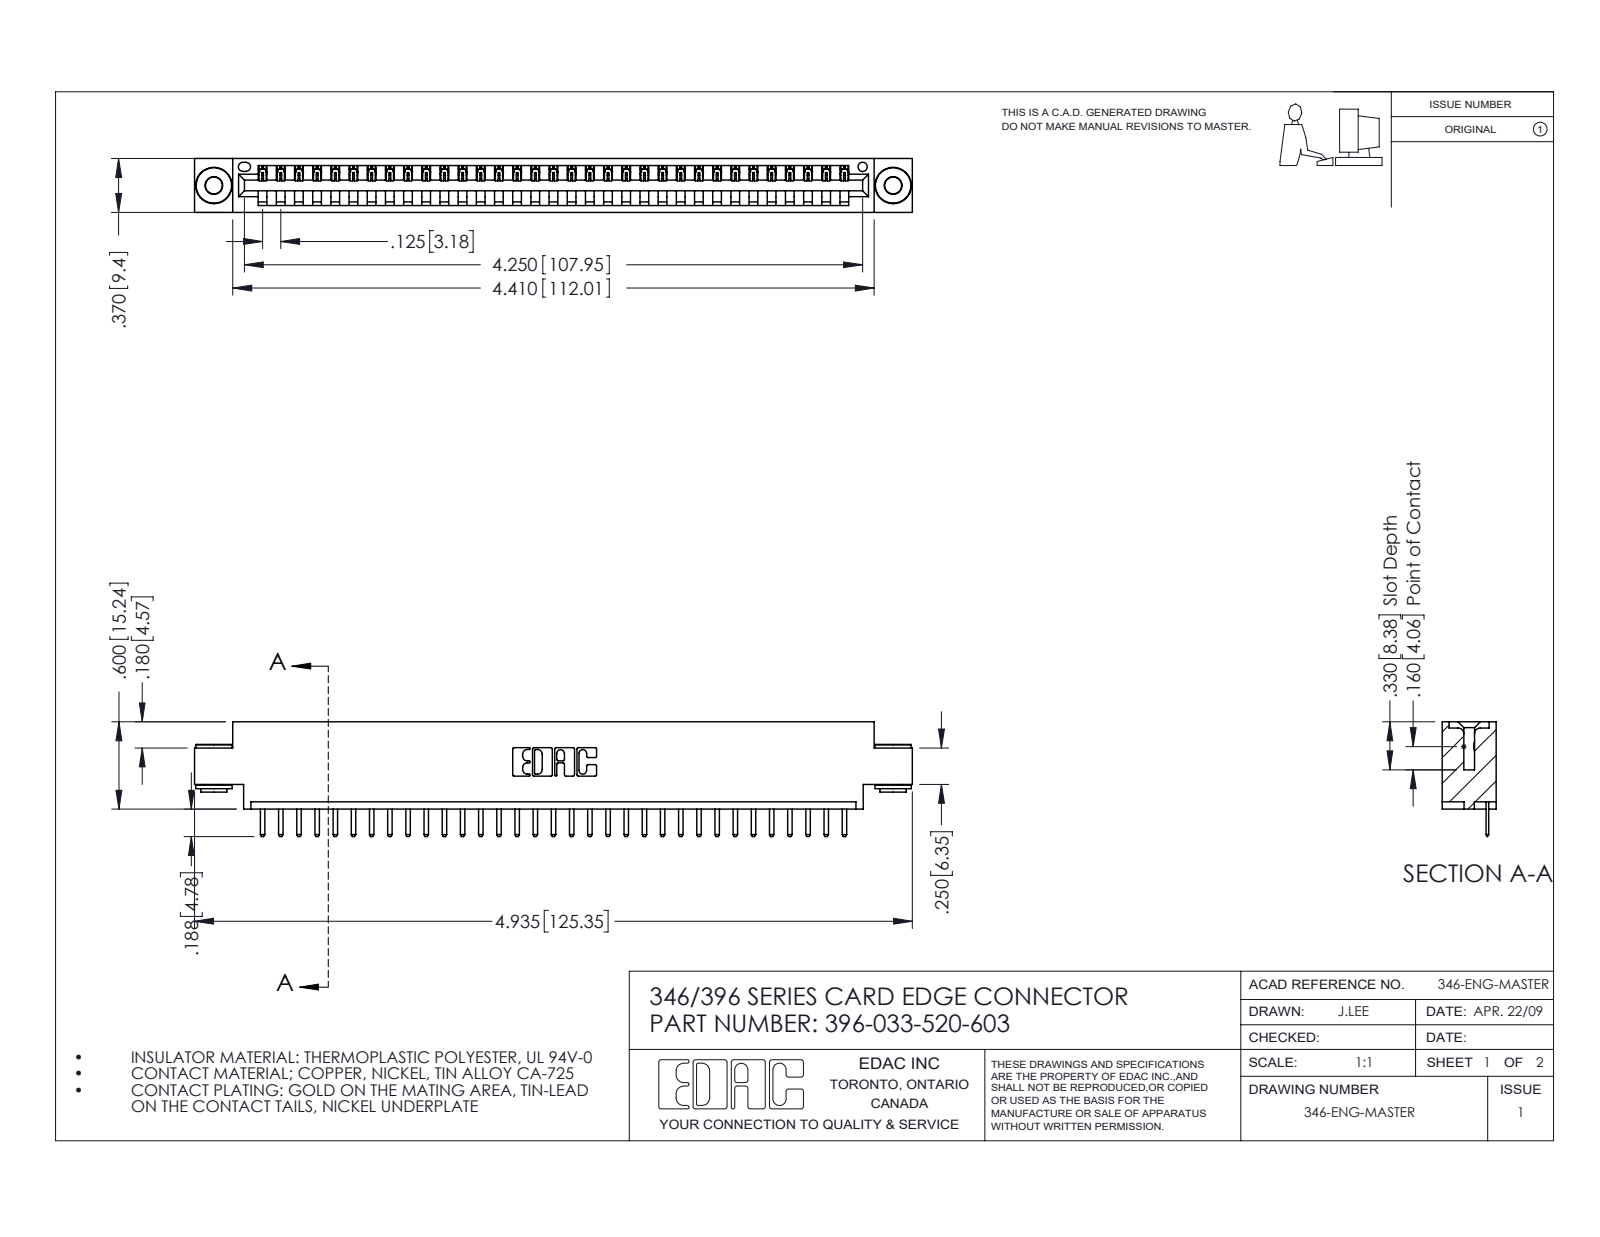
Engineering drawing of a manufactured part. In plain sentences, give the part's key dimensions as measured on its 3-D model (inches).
The part is named "345-250-002_345-250-002-102; 396-033-520-603; 346 Part_0.170 Offset - 0.156 Dia-TH; 345-292-001_345-293-120". Its 3-D file was written by "SolidWorks 2016 (CONFIG_CONTROL_DESIGN)". It is 36 solids with 2210 faces: 1476 planar, 726 cylindrical and 8 other. Overall it measures 4.935 by 0.788 by 0.37 inches. Its volume is 0.714 cubic inches and its surface area 22.63 square inches. Round holes: 2 of diameter 0.116, 2 of diameter 0.156, 1 of diameter 0.064. Round bosses or shafts: 2 of diameter 0.25, 2 of diameter 0.18, 2 of diameter 0.136. Partial cylindrical surfaces (rounded edges, fillets, slot ends): 68 of radius 0.01, 66 of radius 0.006, 22 of radius 0.01, 6 of radius 0.007, 6 of radius 0.031, 3 of radius 0.026, 2 of radius 0.031, 2 of radius 0.04. The main face-to-face distances are 0.048, 0.322, 0.37, 0.25, 0.025, 0.148, 0.222, 0.1, 0.174, 0.072. The hole center spacings are 0.246, 4.462, 4.67.
